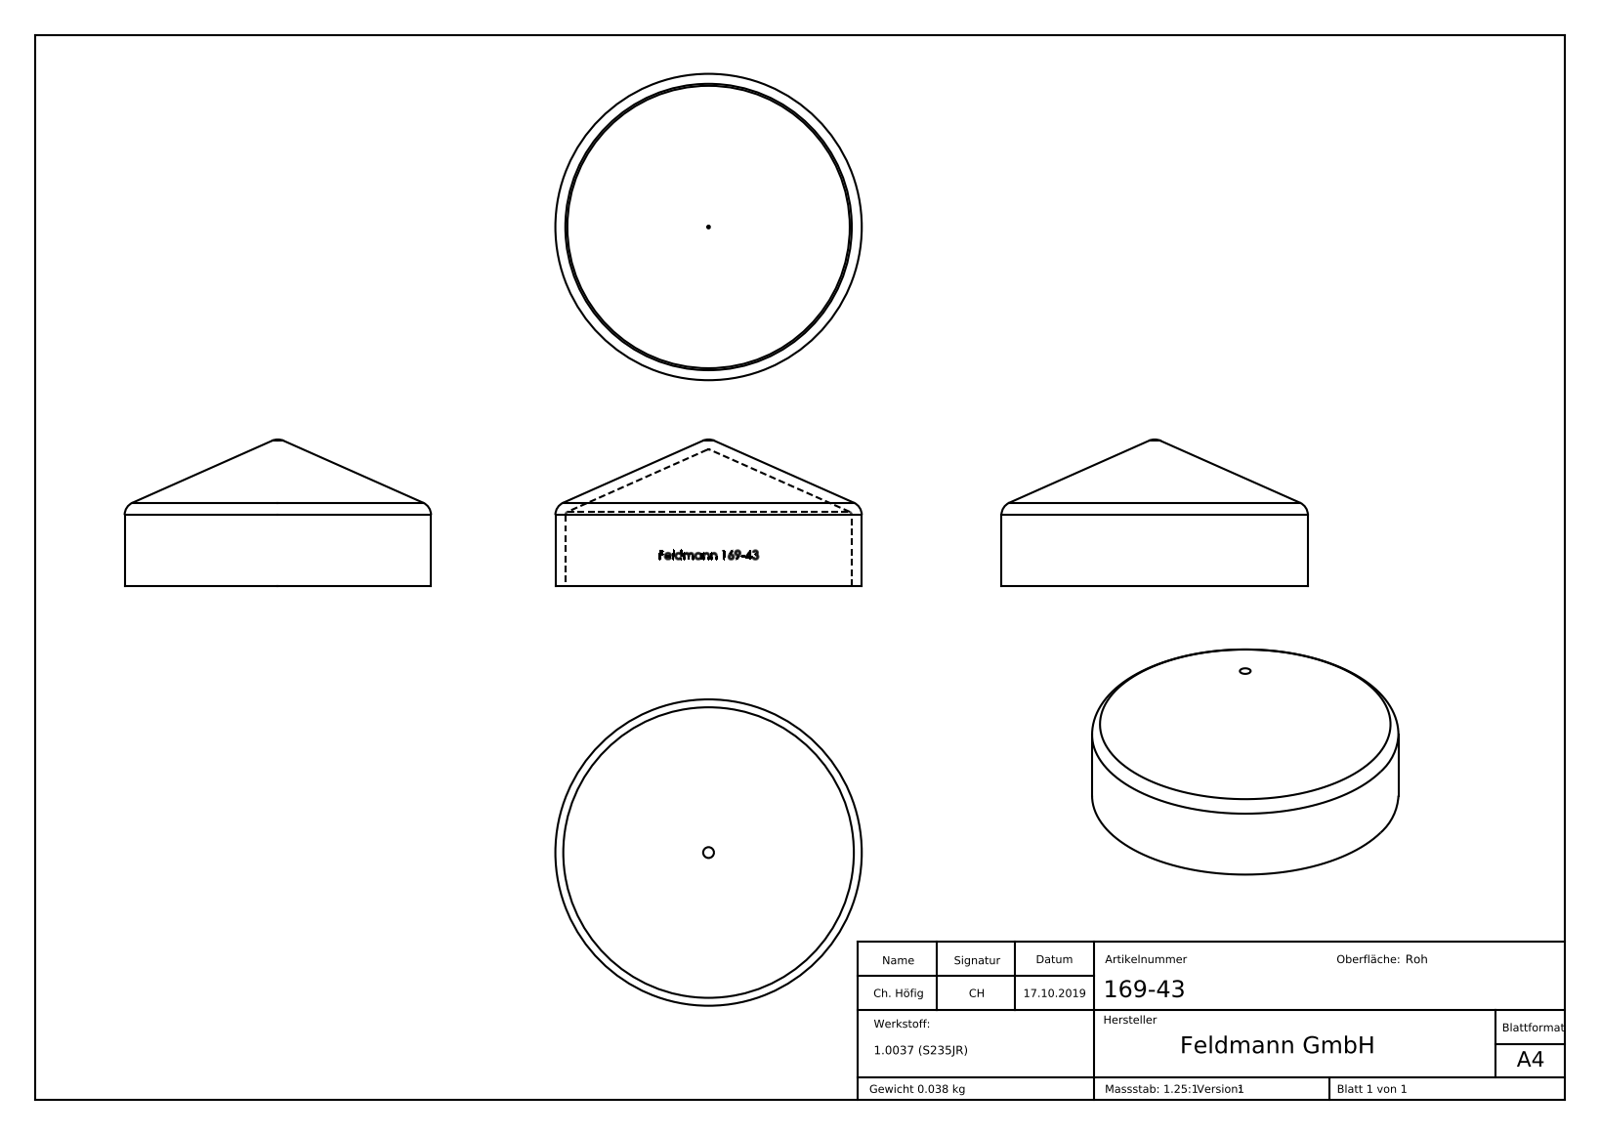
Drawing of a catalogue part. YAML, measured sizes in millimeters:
part_name: "169-43"
step_written_by: "SolidWorks 2015 (CONFIG_CONTROL_DESIGN)"
units: millimeters
bodies: {solids: 1, faces: 195, planar: 87, cylindrical: 22, other: 86}
overall_size: [46, 46, 22]
volume: 4923
surface_area: 6787
round_holes:
  - {diameter: 43, count: 1}
round_bosses_or_shafts:
  - {diameter: 46, count: 1}
partial_cylinders:
  - {radius: 21.6, count: 1}
face_to_face_distances: [4, 0.39, 2.02, 11.57, 1.26, 1.65, 13.59, 10.31, 2.97, 2.96]
